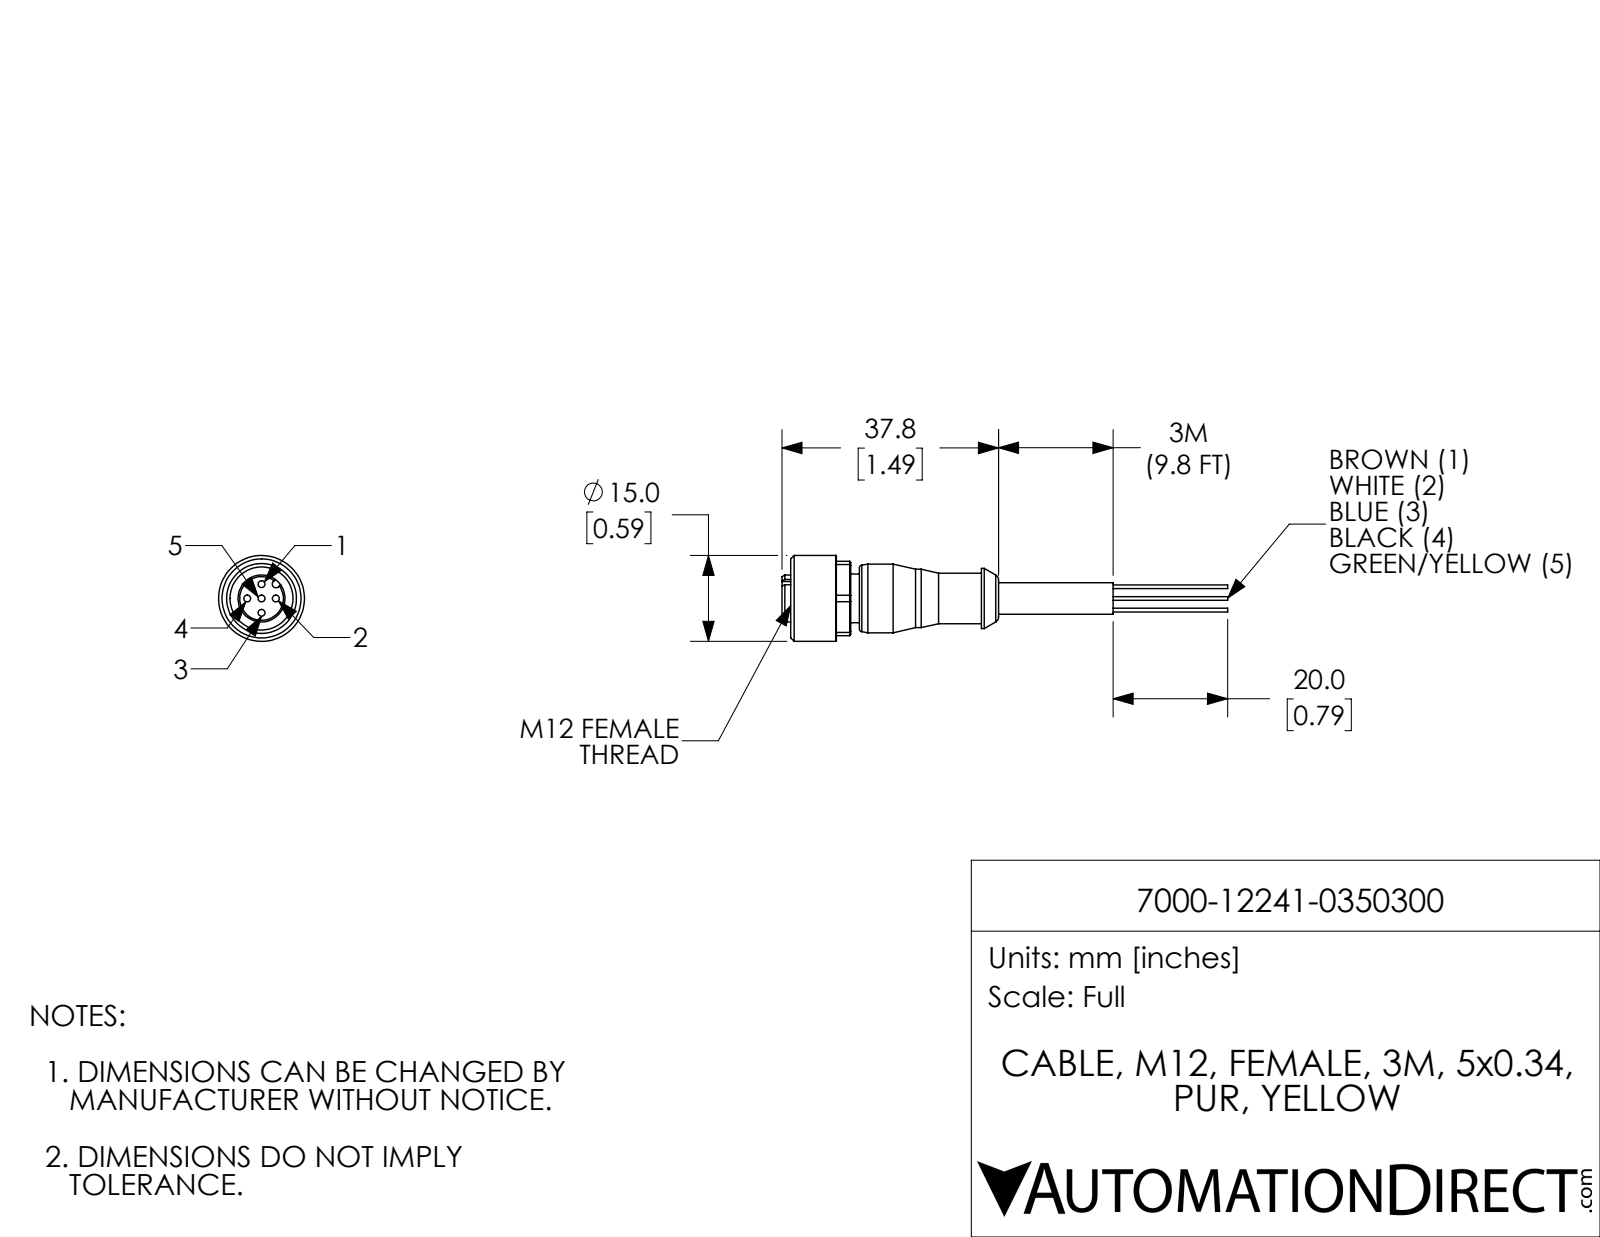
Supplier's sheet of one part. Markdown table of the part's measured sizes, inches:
| quantity | value |
| --- | --- |
| part name | 7000-12241-0350300 |
| STEP written by | SolidWorks 2021 (CONFIG_CONTROL_DESIGN) |
| units | inches |
| bodies | 1 solid, 106 faces (34 planar, 45 cylindrical, 27 other) |
| overall size | 3.063 × 0.591 × 0.591 |
| volume | 0.248 in³ |
| surface area | 4.45 in² |
| round holes (diameter × count) | 0.047 × 5, 0.433 × 1 |
| round bosses / shafts (diameter × count) | 0.026 × 5, 0.591 × 1, 0.472 × 1, 0.413 × 1, 0.402 × 1, 0.346 × 1, 0.335 × 1, 0.323 × 1 |
| partial cylindrical surfaces (radius × count) | 0.026 × 1, 0.283 × 1 |
| main face-to-face distances | 0.472, 0.059, 0.118, 0.512, 0.354, 1.016, 0.295, 0.413, 0.098, 0.531 |
| hole center spacings | 0.098, 0.139, 0.197 |
